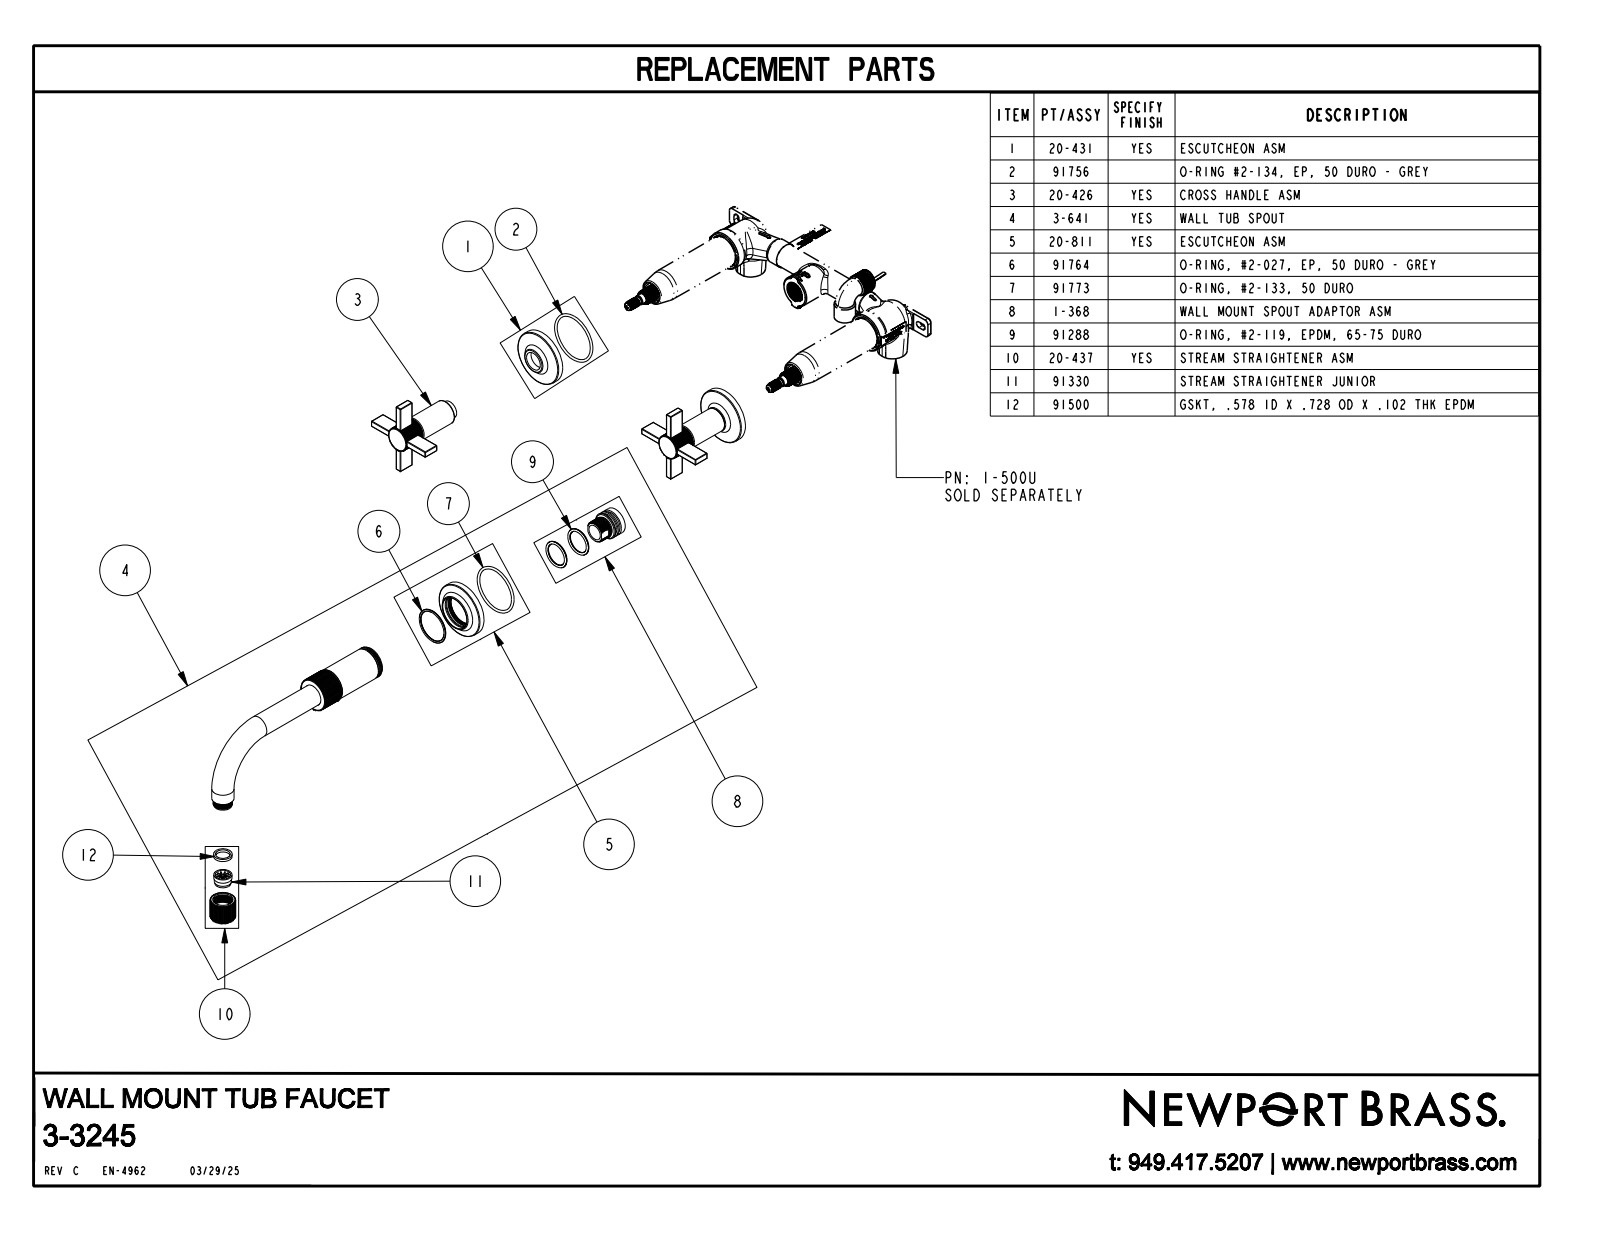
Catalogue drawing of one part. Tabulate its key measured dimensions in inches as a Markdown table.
| quantity | value |
| --- | --- |
| part name | 3-3245_SW0001 |
| STEP written by | CREO PARAMETRIC BY PTC INC, 2018400 (AUTOMOTIVE_DESIGN) |
| units | inches |
| bodies | 3 solids, 1407 faces (739 planar, 522 cylindrical, 146 other) |
| overall size | 10.875 × 10.76 × 8.75 |
| volume | 17.99 in³ |
| surface area | 101.5 in² |
| round bosses / shafts (diameter × count) | 2.25 × 3, 1 × 2, 0.875 × 2, 0.85 × 2, 0.52 × 2, 1.312 × 1, 1.28 × 1 |
| partial cylindrical surfaces (radius × count) | 0.02 × 68, 0.03 × 12, 0.436 × 2, 0.5 × 1, 0.675 × 1 |
| main face-to-face distances | 0.25, 7.875, 2.496, 3.146, 0.65, 3.201, 0.705, 0.055, 8.125, 7.625 |
